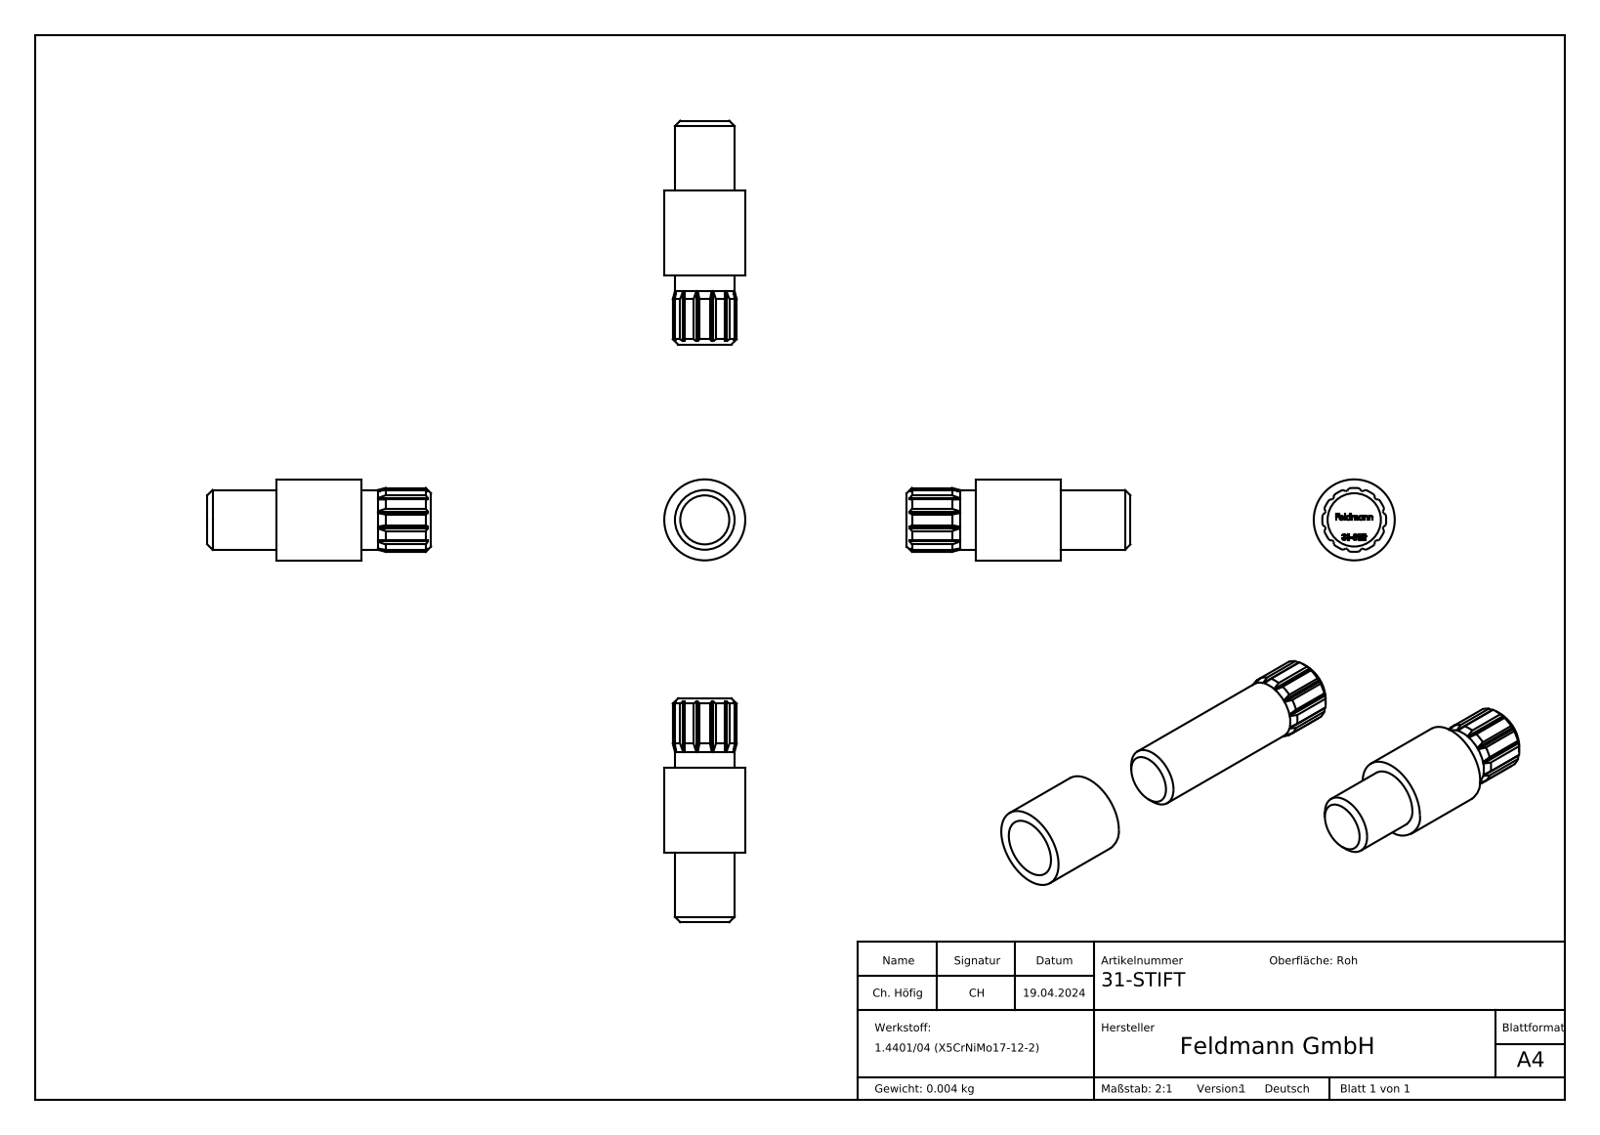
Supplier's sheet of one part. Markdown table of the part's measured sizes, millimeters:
| quantity | value |
| --- | --- |
| part name | 31-STIFT; 31-STIFT Teil2_31-STIFT Teil2; 31-STIFT Teil1_31-STIFT Teil1 |
| STEP written by | SolidWorks 2018 (CONFIG_CONTROL_DESIGN) |
| units | millimeters |
| bodies | 2 solids, 271 faces (157 planar, 15 cylindrical, 99 other) |
| overall size | 21 × 7.6 × 7.6 |
| volume | 692 mm³ |
| surface area | 801 mm² |
| round holes (diameter × count) | 5.6 × 1 |
| round bosses / shafts (diameter × count) | 7.6 × 1 |
| partial cylindrical surfaces (radius × count) | 3 × 1 |
| main face-to-face distances | 6.5, 14.5, 8, 21, 4.04, 4.02, 6.4, 14.4, 20.9, 0.63 |
